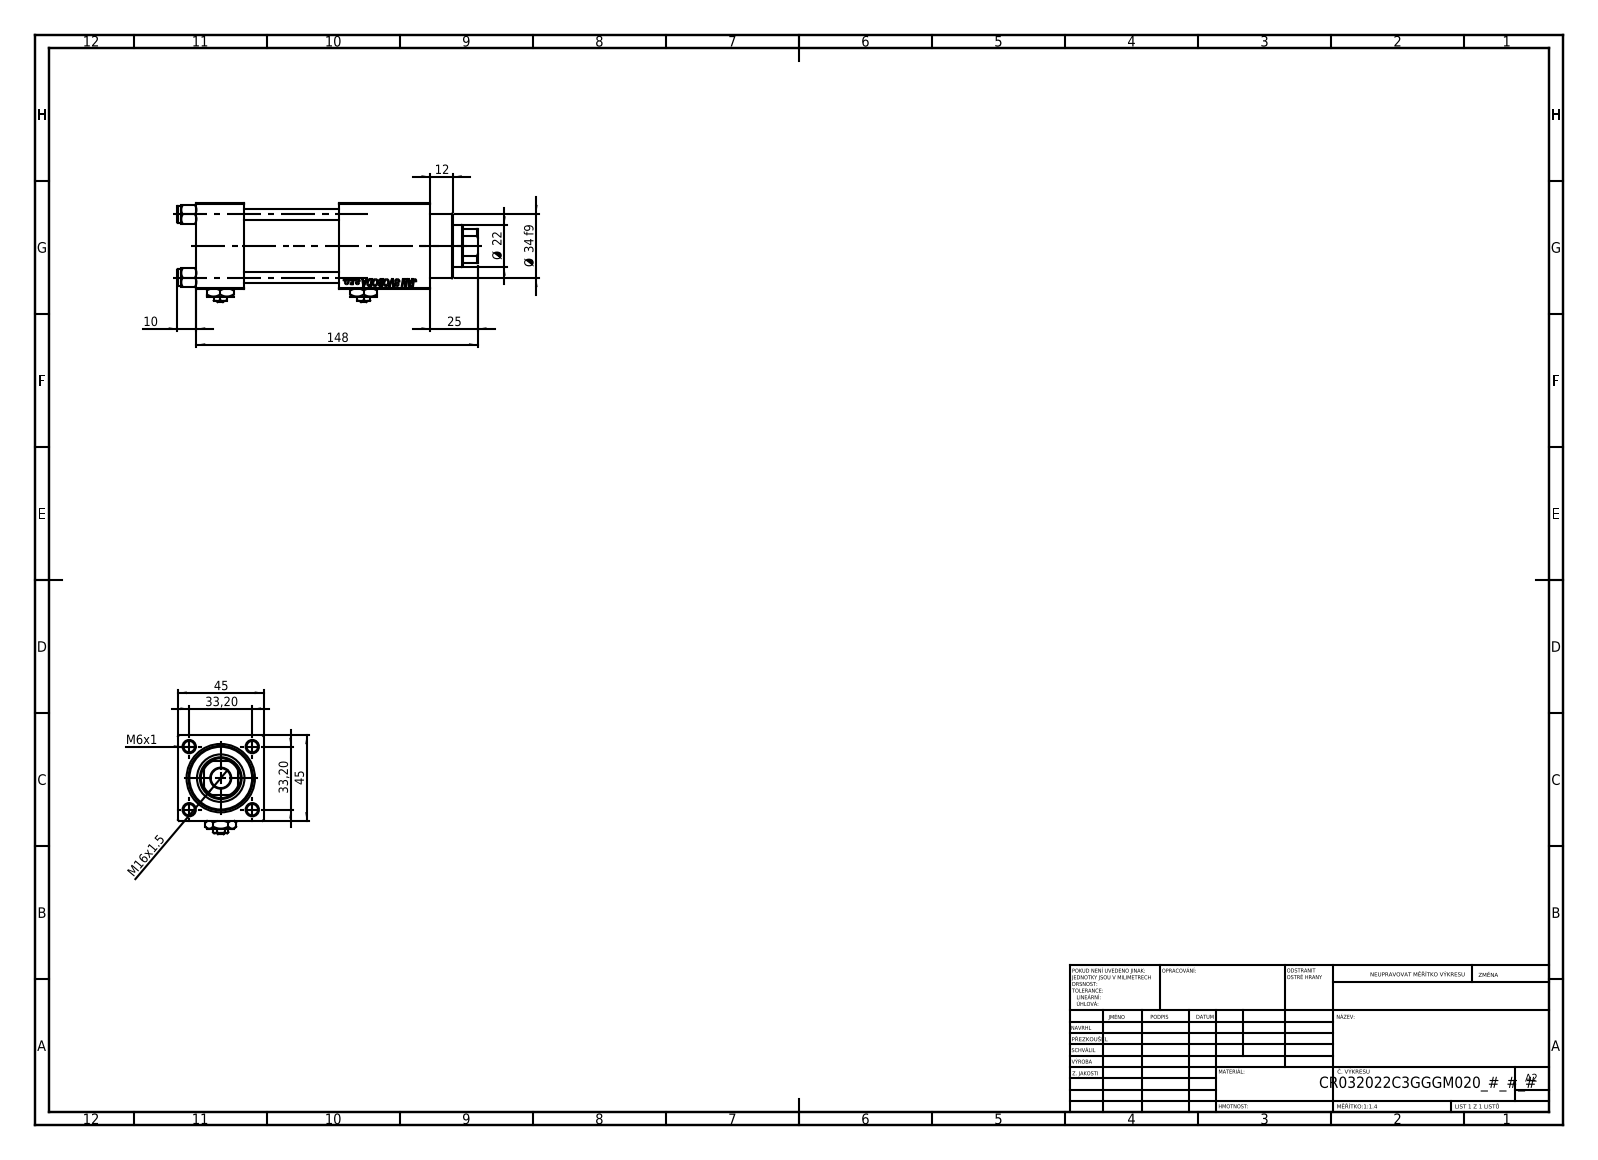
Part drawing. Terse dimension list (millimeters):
name: V215CR_VCP_C; Zatka_pro_OIL_PORT; V215CR_C_Body; V215_VC_A (+2 more)
written by: SolidWorks 2019 (CONFIG_CONTROL_DESIGN)
unit: mm
bodies: 13 solids, 1248 faces (572 planar, 98 cylindrical, 578 other)
size: 158 × 52 × 45
volume: 207 903 mm³; area: 73 208 mm²
holes: 4× ⌀6, 2× ⌀7, 2× ⌀13.16, 2× ⌀20, 1× ⌀10.5, 1× ⌀22, 1× ⌀24, 1× ⌀25, 1× ⌀32, 1× ⌀33
bosses: 4× ⌀9, 1× ⌀38, 1× ⌀34
rounds: 1× R10.5
face distances: 45, 25, 50, 123, 75, 98, 44.8, 48, 94.3, 69.3
hole spacings: 23.48, 33.2, 46.95, 75.5
